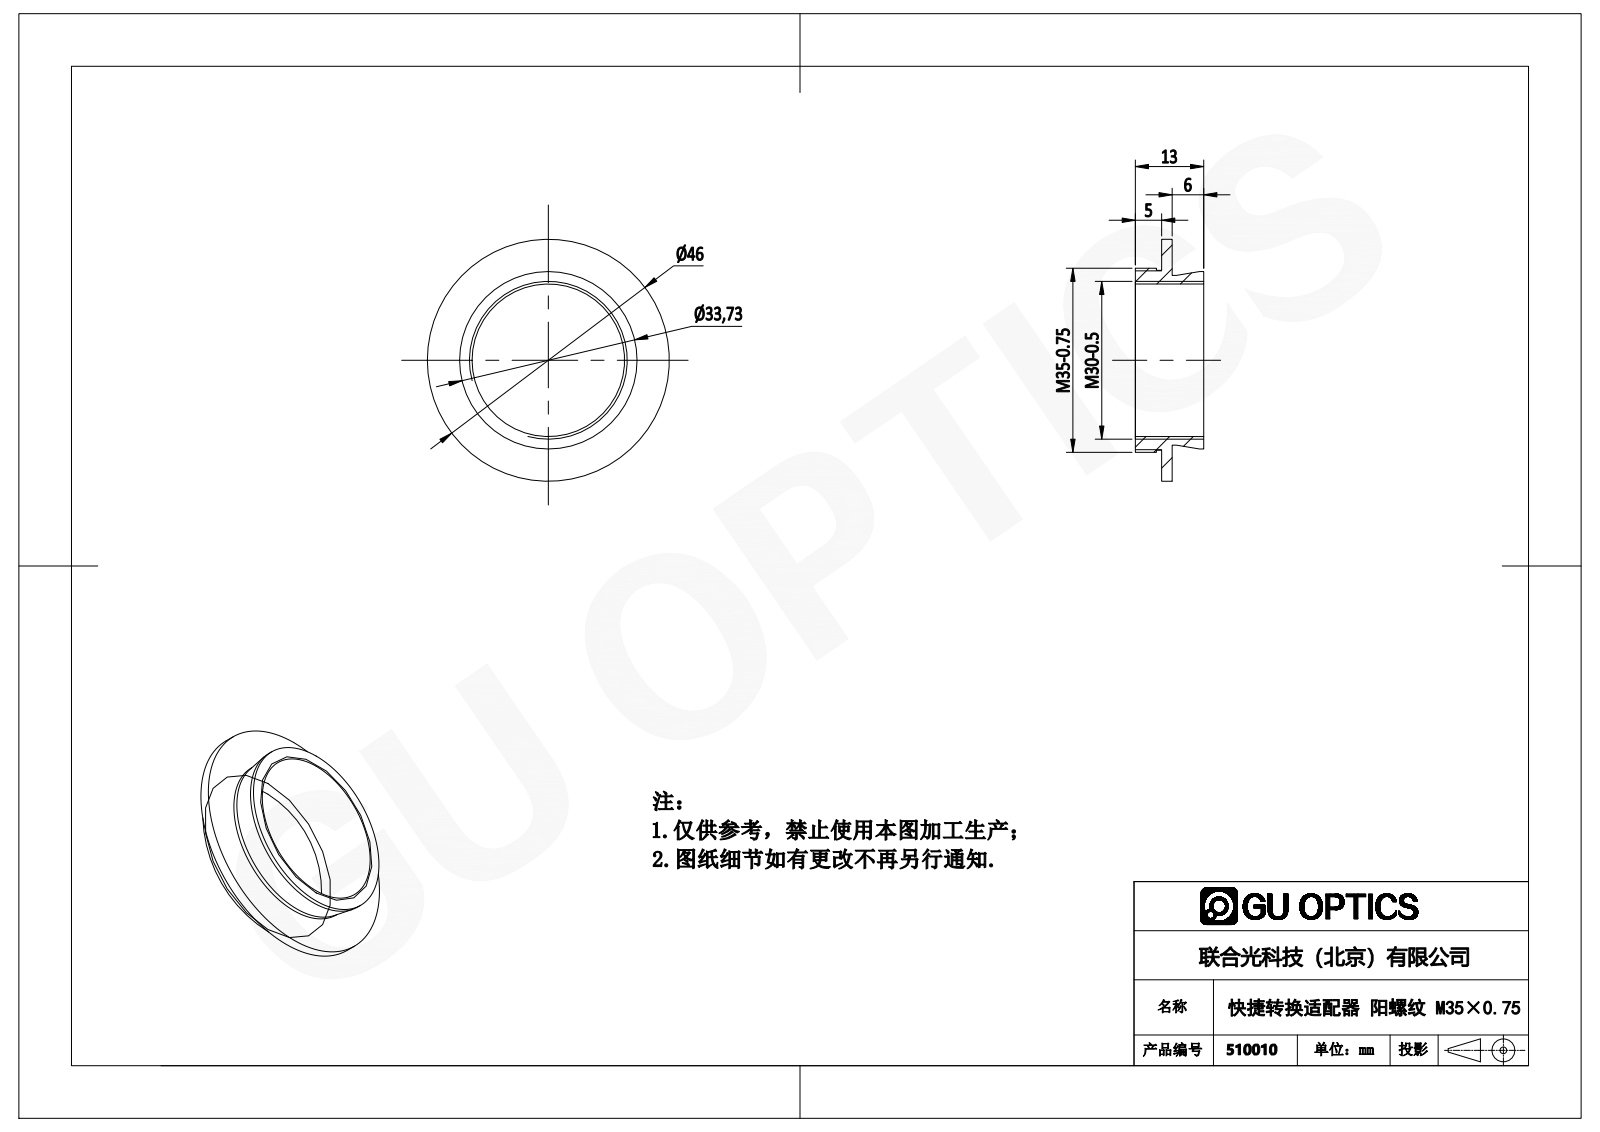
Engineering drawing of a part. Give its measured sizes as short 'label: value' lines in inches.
name: 510010
written by: SolidWorks 2016 (CONFIG_CONTROL_DESIGN)
unit: in
bodies: 1 solid, 19 faces (5 planar, 12 cylindrical, 2 other)
size: 1.811 × 1.811 × 0.512
volume: 0.283 in³; area: 7.462 in²
holes: 1× ⌀1.142
bosses: 1× ⌀1.811, 1× ⌀1.378, 1× ⌀1.346, 1× ⌀1.328, 1× ⌀1.27
face distances: 0.079, 0.197, 0.276, 0.512, 0.315, 0.236, 0.157, 0.039, 0.118, 0.354
